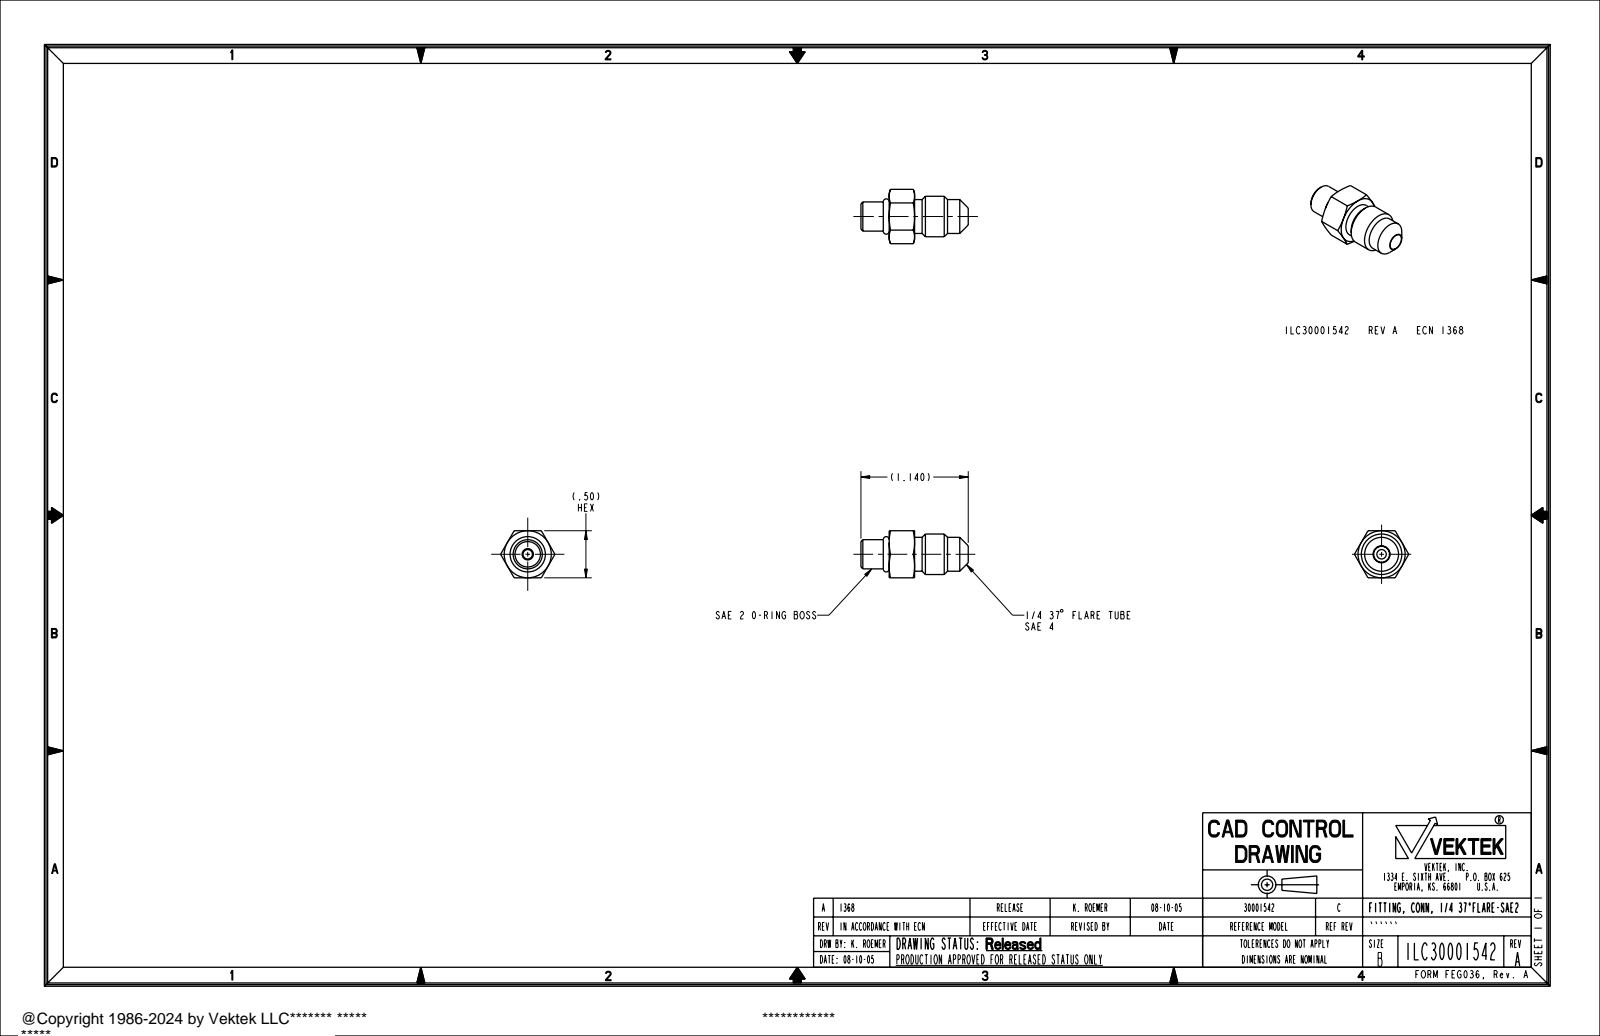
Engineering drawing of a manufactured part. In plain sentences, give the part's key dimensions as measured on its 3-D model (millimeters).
The part is named "ILC30001542". Its 3-D file was written by "PRO/ENGINEER BY PARAMETRIC TECHNOLOGY CORPORATION, 2004290 (AUTOMOTIVE_DESIGN_CC2)". It is 1 solid with 47 faces: 11 planar, 12 cylindrical and 24 other. Overall it measures 29 by 14.7 by 12.7 millimeters. Its volume is 2 080 cubic millimeters and its surface area 1 537 square millimeters. Round holes: 1 of diameter 2.5, 1 of diameter 4.3. Round bosses or shafts: 1 of diameter 10.9, 1 of diameter 9.1, 1 of diameter 7.9. The main face-to-face distances are 12.7, 6.9, 14.5, 7.6, 4.6, 2.3, 9.9, 19.1, 21.3, 29.
